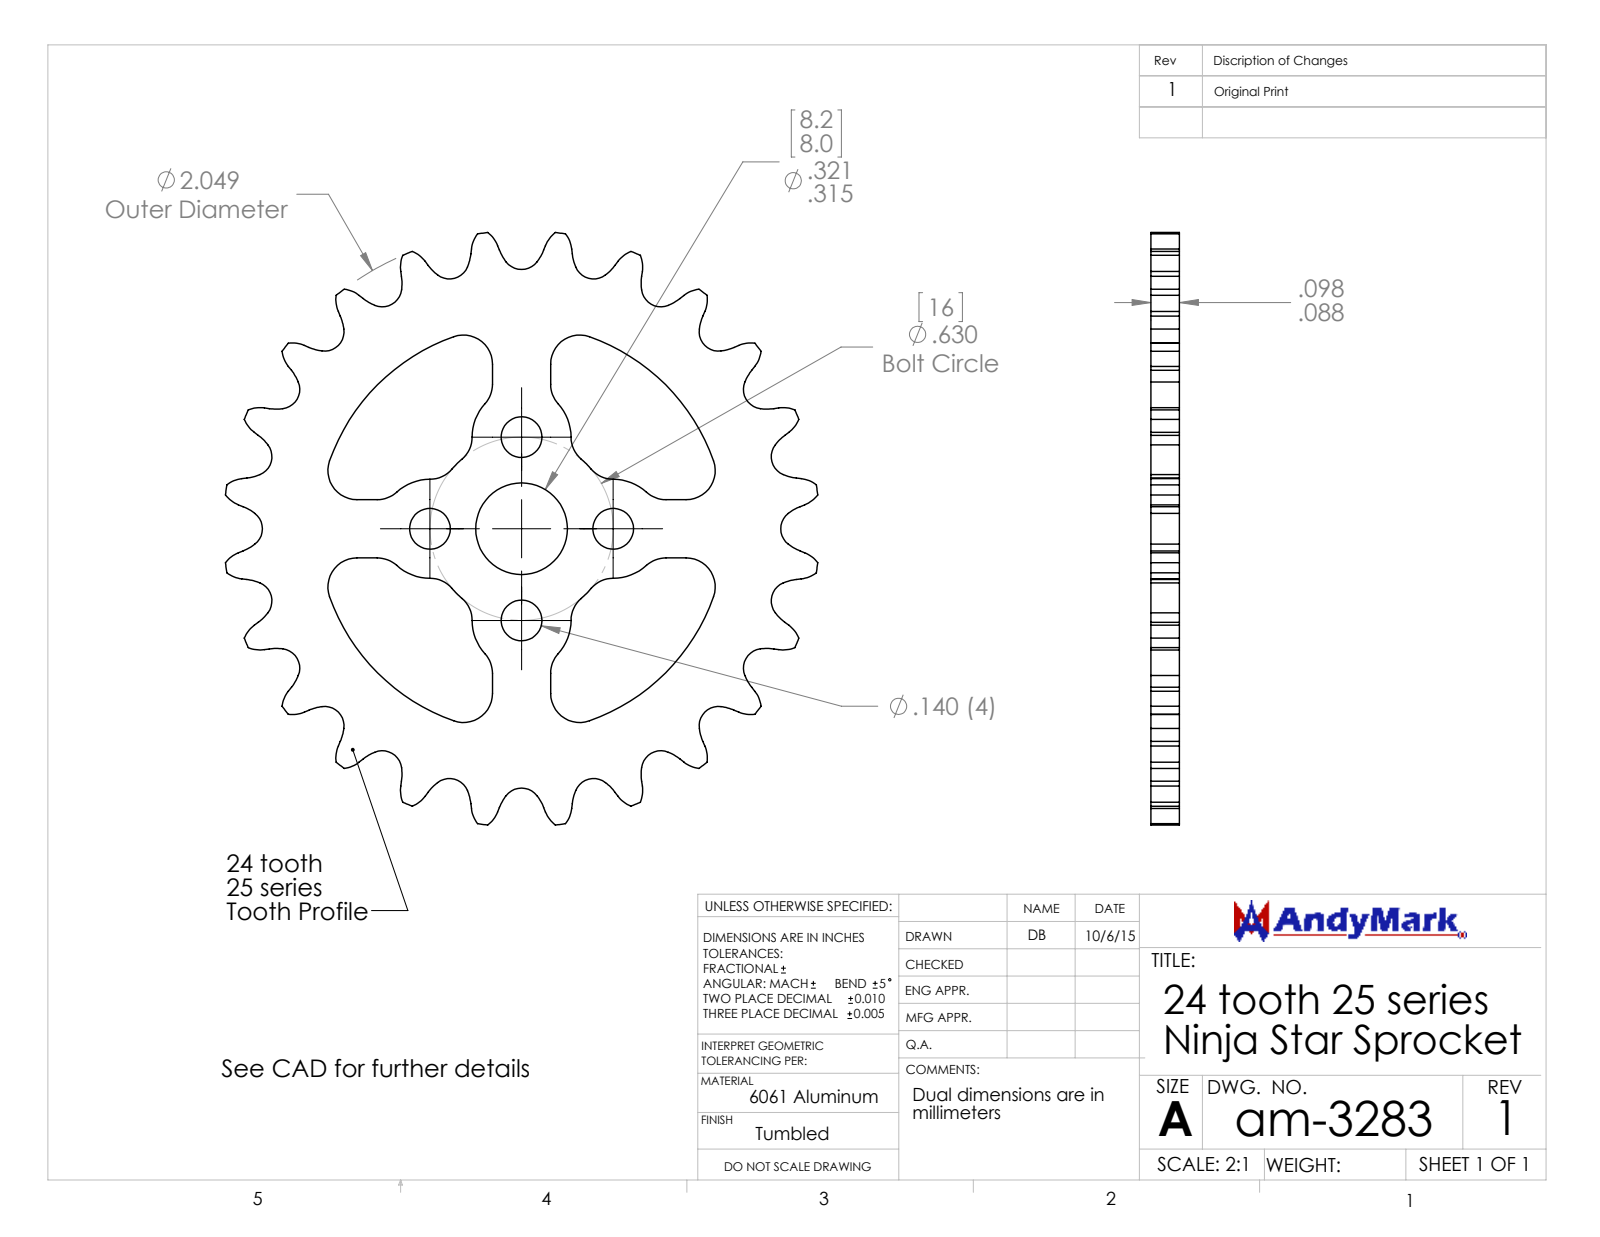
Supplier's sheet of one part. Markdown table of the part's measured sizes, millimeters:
| quantity | value |
| --- | --- |
| part name | am-3283 24t Ninja Star Sprocket |
| STEP written by | SolidWorks 2014 (AUTOMOTIVE_DESIGN) |
| units | millimeters |
| bodies | 1 solid, 267 faces (58 planar, 209 cylindrical, 0 other) |
| overall size | 51.7 × 51.7 × 2.5 |
| volume | 3 030 mm³ |
| surface area | 3 654 mm² |
| round holes (diameter × count) | 3.6 × 4, 8 × 1 |
| partial cylindrical surfaces (radius × count) | 2.7 × 48, 4.3 × 48, 1.7 × 24, 2.5 × 24, 4.3 × 4, 8 × 1, 17.8 × 1, 26 × 1 |
| main face-to-face distances | 2.5, 14.5, 5.1, 14.5 |
| hole center spacings | 8, 11.3, 16 |
